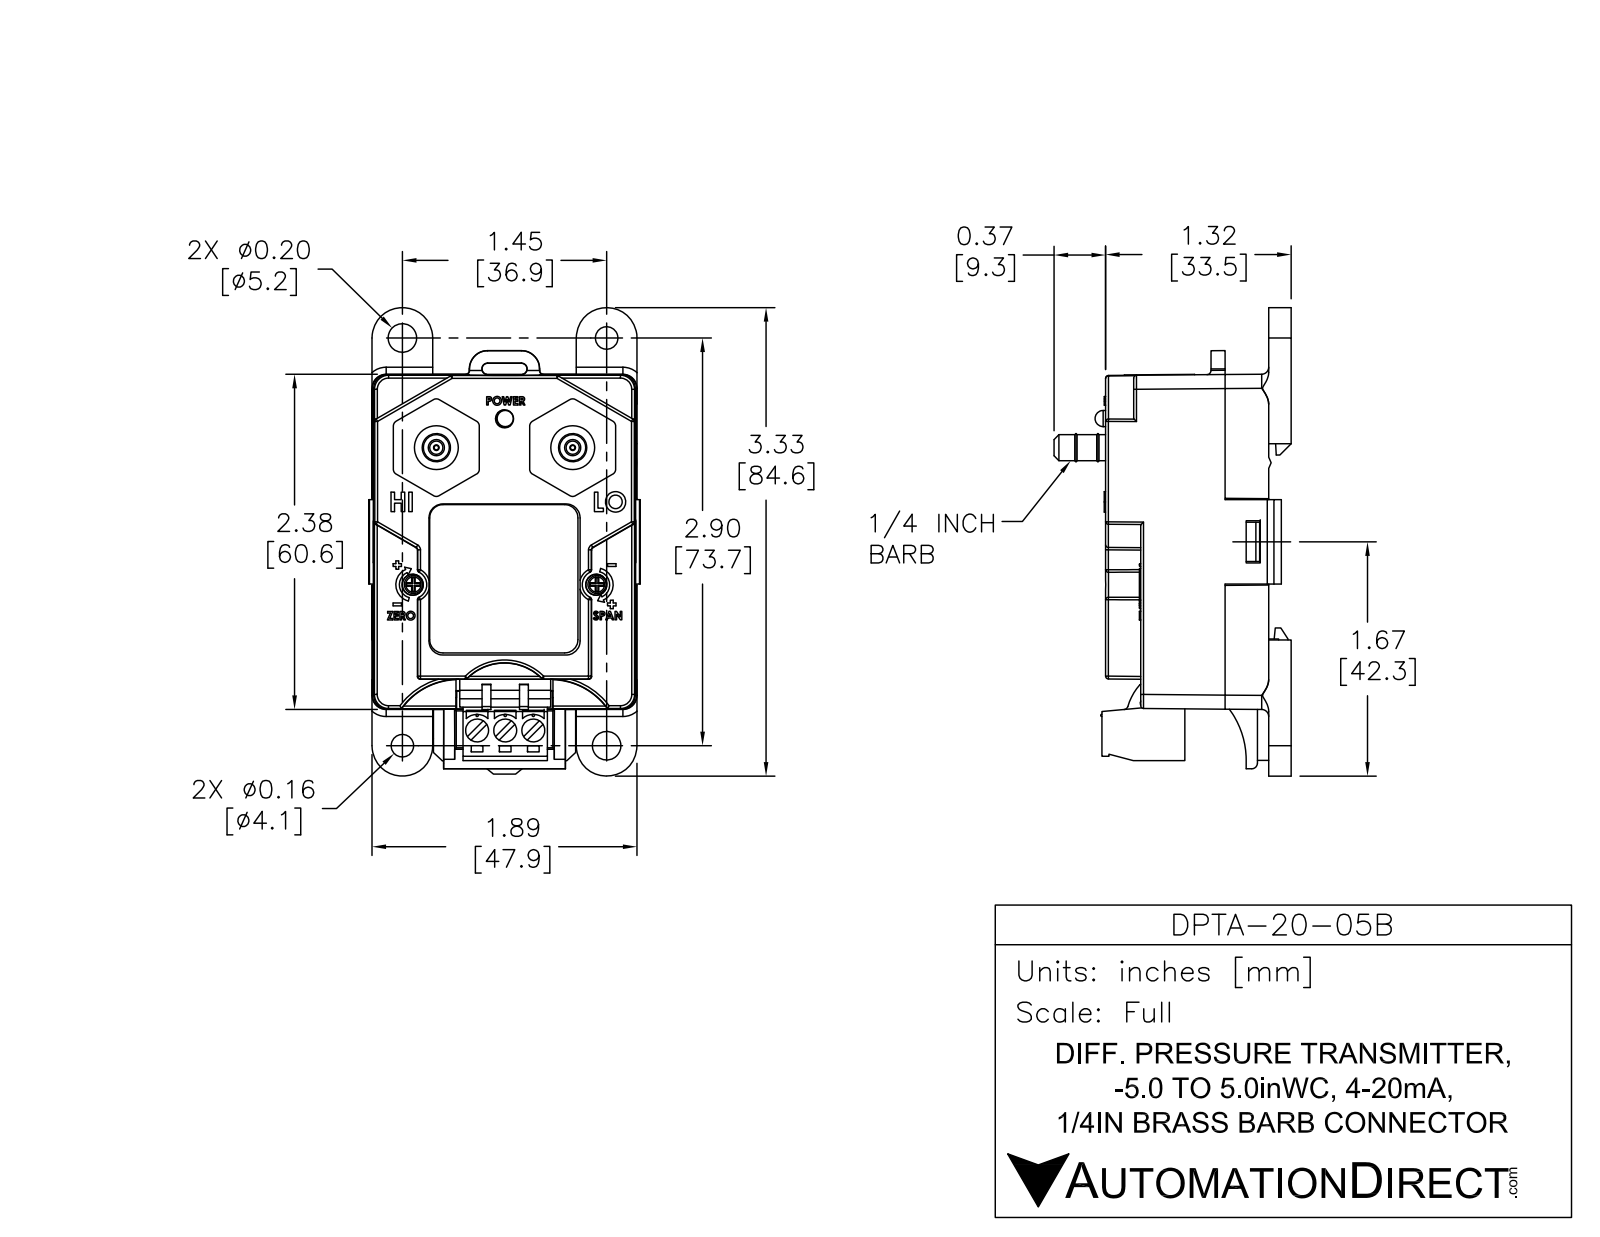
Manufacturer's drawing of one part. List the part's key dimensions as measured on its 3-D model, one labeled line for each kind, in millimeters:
Part name (STEP PRODUCT): DPTA-20-05B
STEP written by: SolidWorks 2011 (AUTOMOTIVE_DESIGN)
Units: millimetres
Bodies: 11 solids, 448 faces (354 planar, 85 cylindrical, 9 other)
Overall size (bounding box): 85.01 × 49.76 × 43.1
Volume: 29 684 mm³ · Surface area: 34 743 mm²
Round holes (diameter × count): ⌀4 ×7, ⌀2.5 ×2, ⌀5.12 ×2, ⌀3.1 ×1
Round bosses / shafts (diameter × count): ⌀5 ×3, ⌀3.5 ×3, ⌀3.5 ×3, ⌀8 ×2, ⌀4.75 ×2, ⌀3 ×1
Partial cylindrical surfaces — rounded edges, fillets, slot ends (radius × count): R3 ×12, R2 ×4, R5.5 ×4, R0.99 ×2, R1.06 ×2, R1.12 ×2, R2.38 ×2, R3.25 ×2
Main face-to-face distances: 1, 1.9, 4, 29.1, 0.5, 46.9, 5.9, 5, 33.1, 27.2
Hole centre spacings: 13.55, 20.73, 23.37, 24.92, 29.43, 34.46, 36.67, 38.22
